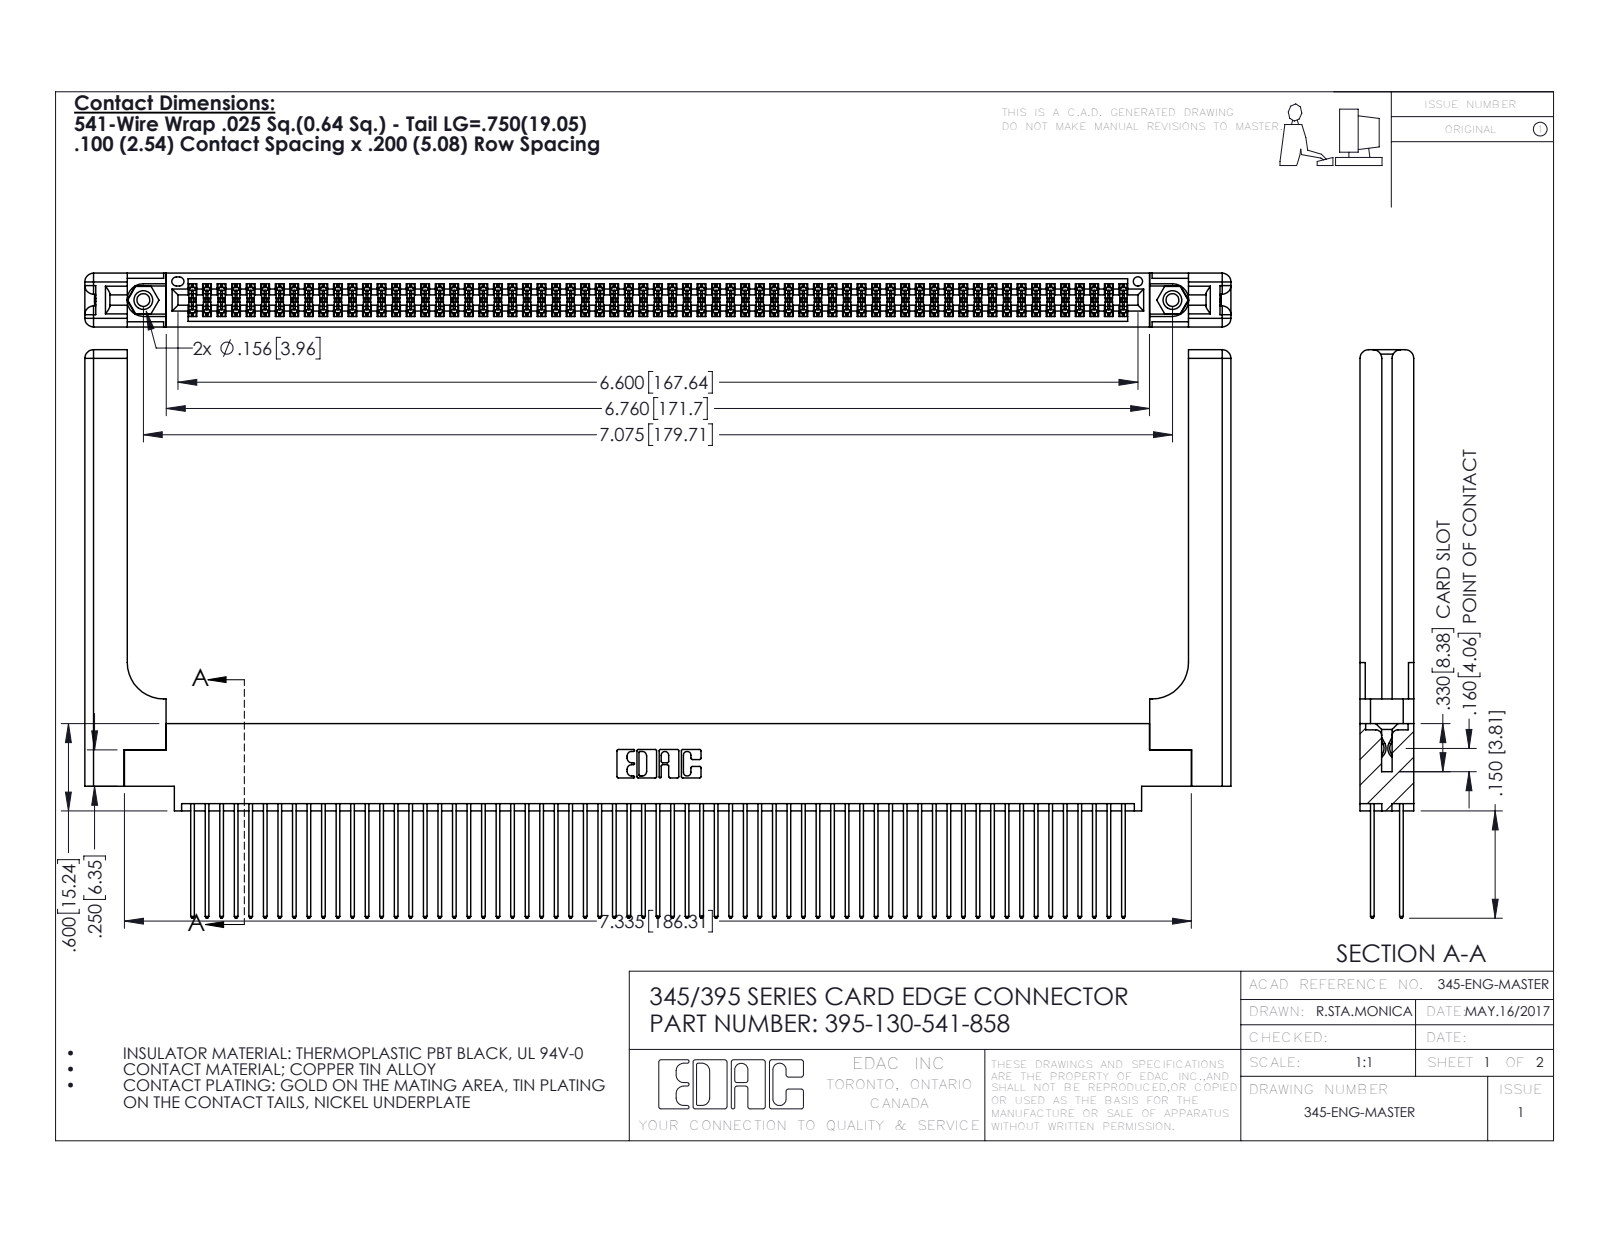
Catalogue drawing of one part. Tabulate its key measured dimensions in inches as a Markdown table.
| quantity | value |
| --- | --- |
| part name | 345-292-001_345-293-141; 345-220-058_345-220-058; 345 Part_0.170 Offset - 0.156 Dia-TH; 345-250-001_345-250-001-102 (+1 more) |
| STEP written by | SolidWorks 2016 (CONFIG_CONTROL_DESIGN) |
| units | inches |
| bodies | 135 solids, 6886 faces (4522 planar, 2304 cylindrical, 60 other) |
| overall size | 7.879 × 3.907 × 0.37 |
| volume | 1.755 in³ |
| surface area | 60.67 in² |
| round holes (diameter × count) | 0.089 × 2, 0.125 × 2, 0.156 × 2, 0.064 × 1 |
| round bosses / shafts (diameter × count) | 0.155 × 2 |
| partial cylindrical surfaces (radius × count) | 0.006 × 195, 0.01 × 130, 0.01 × 22, 0.06 × 16, 0.007 × 6, 0.031 × 6, 0.026 × 3, 0.014 × 2 |
| main face-to-face distances | 0.072, 0.298, 0.098, 0.272, 0.025, 0.2, 0.37, 0.225, 0.175, 0.148 |
| hole center spacings | 0.27, 6.839, 7.075 |
